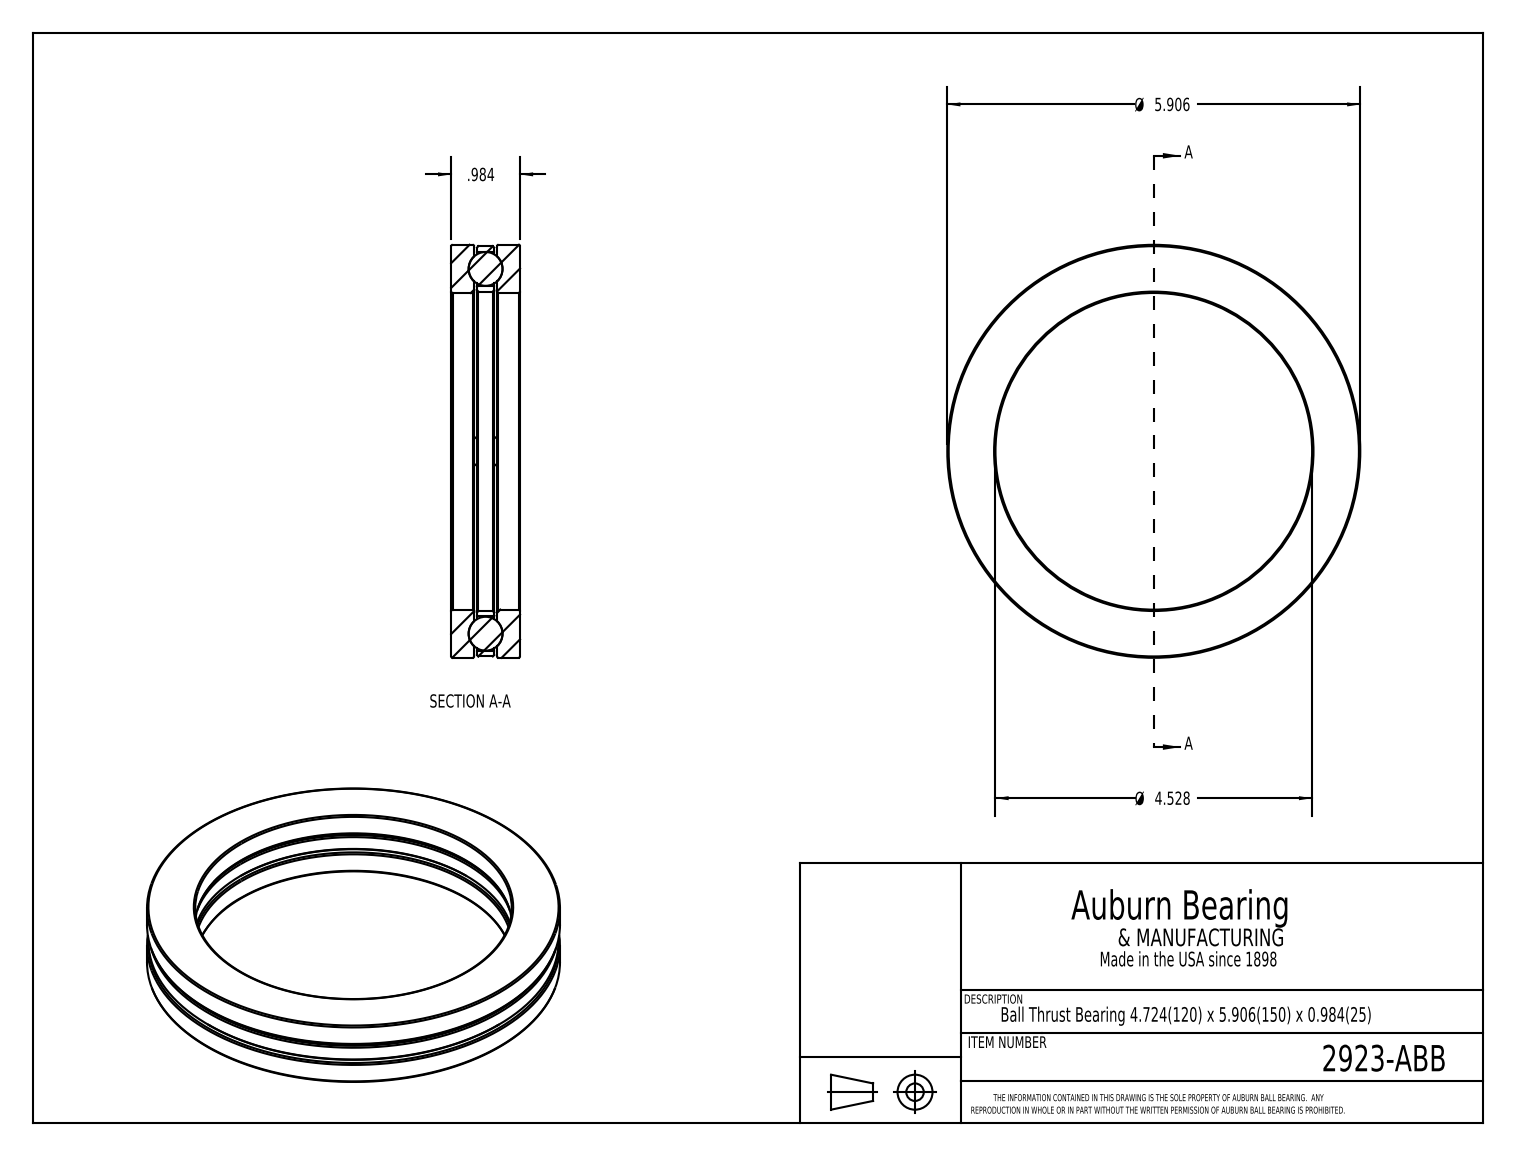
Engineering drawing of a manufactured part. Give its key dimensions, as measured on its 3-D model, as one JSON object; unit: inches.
{"part_name": "2923-ABB", "step_written_by": "SolidWorks 2017 (CONFIG_CONTROL_DESIGN)", "units": "inches", "bodies": {"solids": 7, "faces": 36, "planar": 8, "cylindrical": 10, "other": 18}, "overall_size": [5.906, 5.906, 0.984], "volume_in3": 8.12, "surface_area_in2": 90.47, "round_holes": [[0.494, 4], [4.724, 1], [4.764, 1]], "round_bosses_or_shafts": [[5.906, 1], [5.866, 1]], "face_to_face_distances": [0.369, 0.615, 0.984, 0.246, 0.328, 0.656, 0.041, 0.287, 0.328], "hole_center_spacings": [2.657, 3.758, 5.315]}
